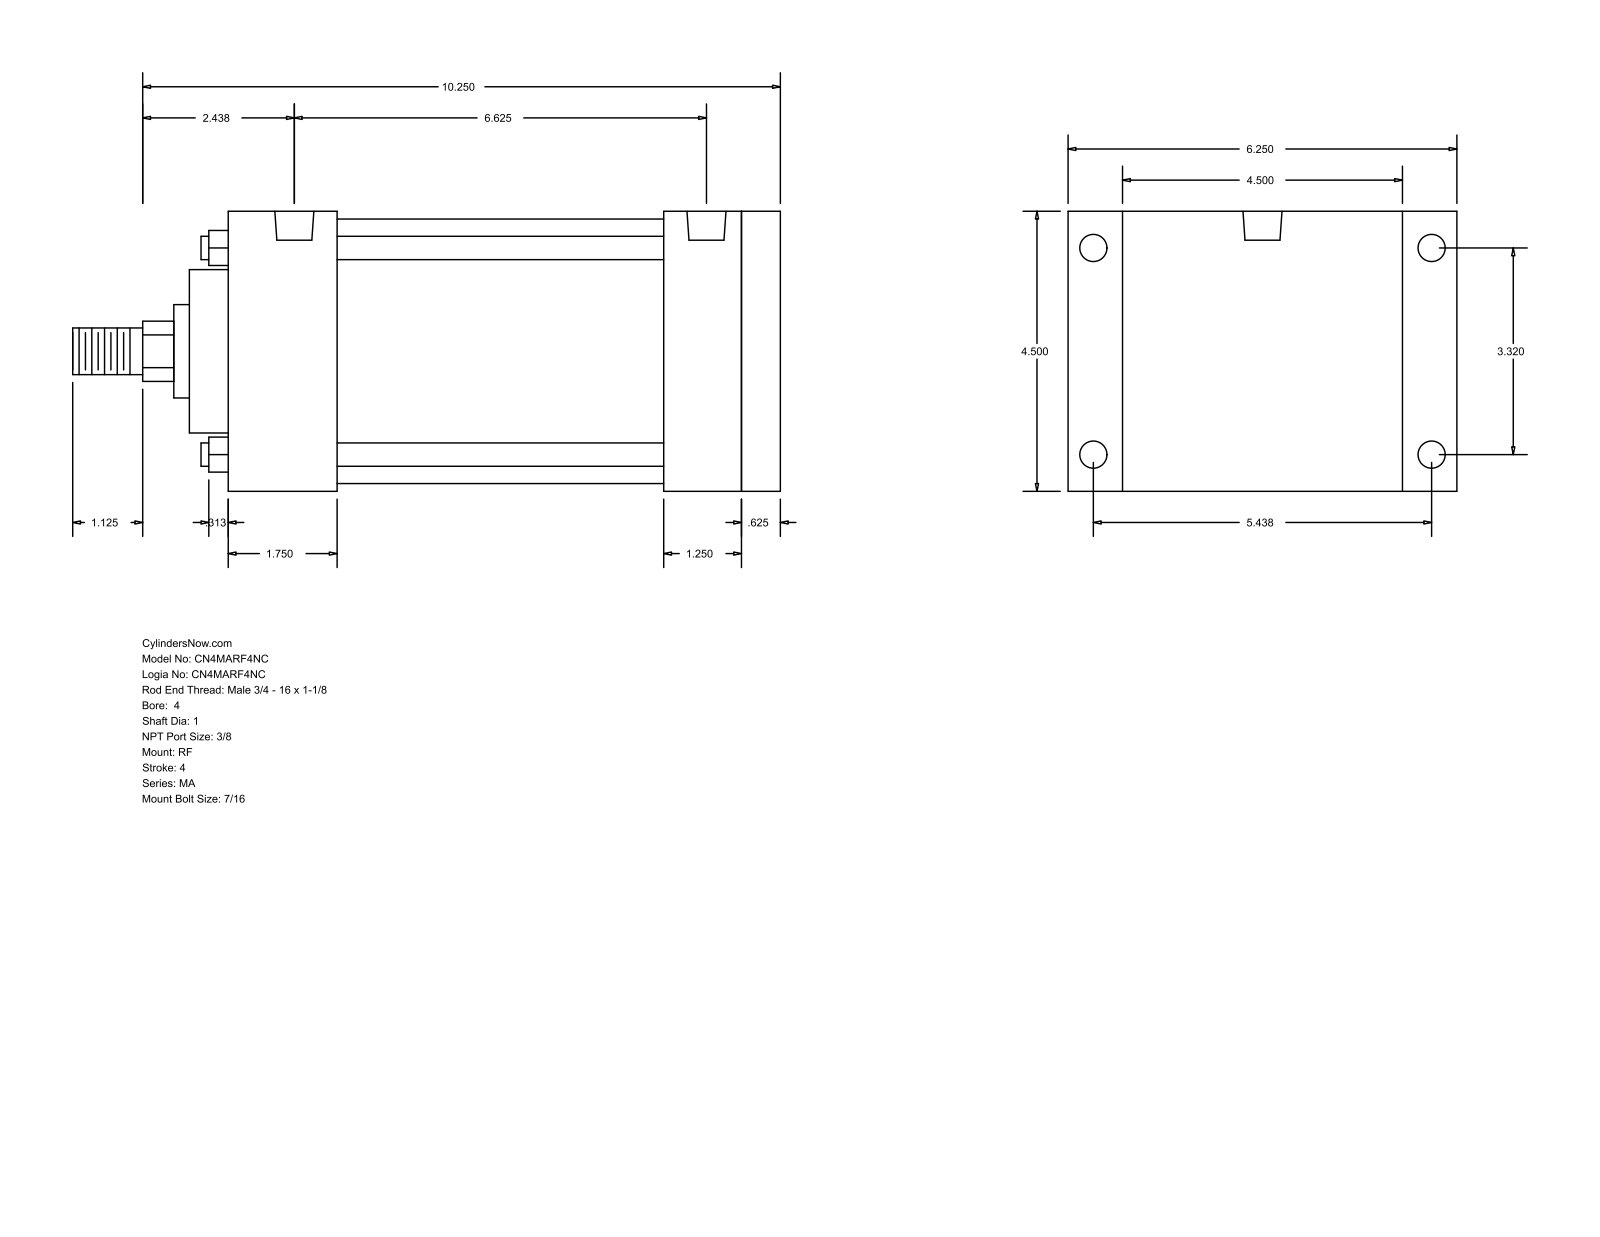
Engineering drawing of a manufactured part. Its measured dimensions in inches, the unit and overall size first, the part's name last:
Units: inches
Overall size (bounding box): 11.375 × 6.25 × 4.5
Round holes (diameter × count): ⌀0.437 ×8, ⌀0.627 ×2
Round bosses / shafts (diameter × count): ⌀0.375 ×4, ⌀4.25 ×1, ⌀2.625 ×1, ⌀1.5 ×1, ⌀1 ×1, ⌀0.75 ×1
Partial cylindrical surfaces — rounded edges, fillets, slot ends (radius × count): R0.484 ×1
Main face-to-face distances: 4.5, 8.875, 8.25, 0.625, 0.875, 5.375, 7, 1.25, 1.875, 1.75
Hole centre spacings: 0.187, 3.32, 5.438, 6.25, 6.371, 6.438, 6.625
Bodies: 0 solids, 94 faces (65 planar, 29 cylindrical, 0 other)
Part name (STEP PRODUCT): MA_RF__0400_1
STEP written by: GSSL Pune (CONFIG_CONTROL_DESIGN)
